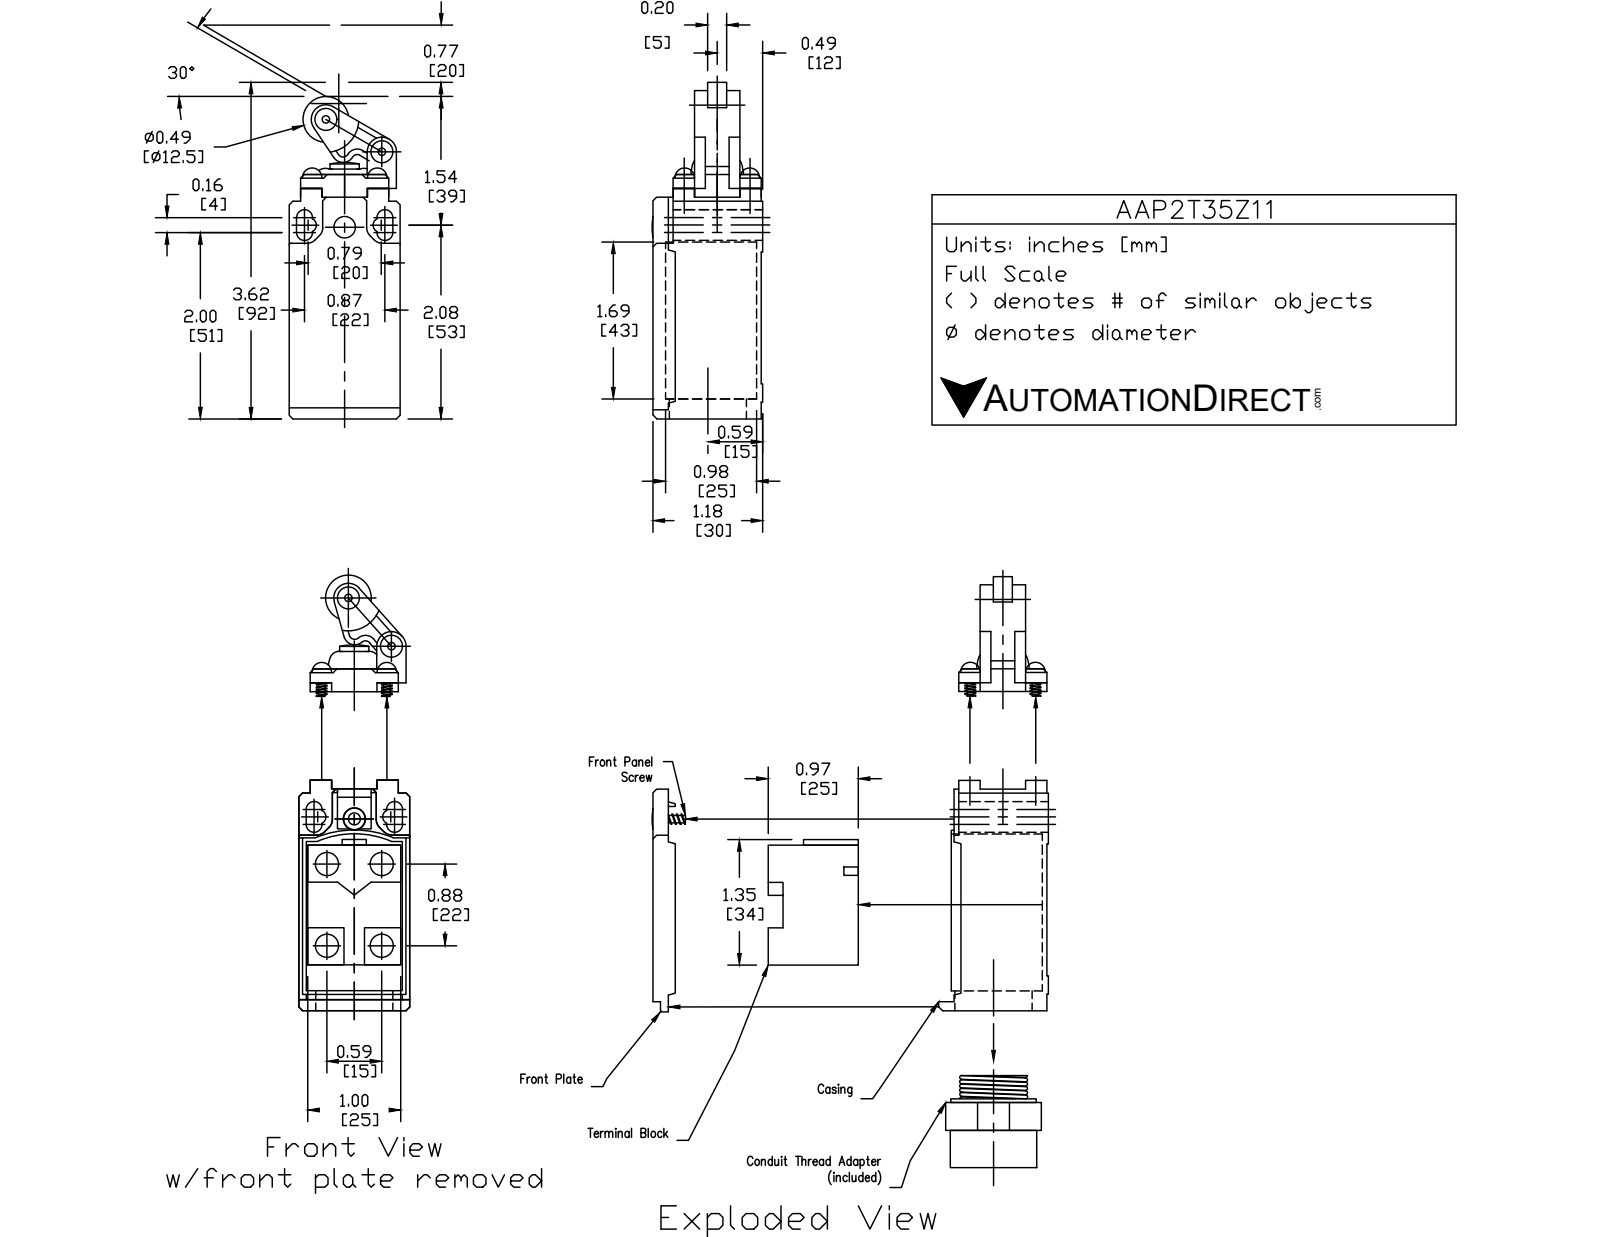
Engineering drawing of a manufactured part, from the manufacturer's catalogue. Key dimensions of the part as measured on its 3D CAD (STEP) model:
Part name (STEP PRODUCT): AAP2T35Z11
STEP written by: SolidWorks 2017 (AUTOMOTIVE_DESIGN)
Units: inches
Bodies: 6 solids, 271 faces (151 planar, 90 cylindrical, 30 other)
Overall size (bounding box): 3.621 × 1.205 × 1.193
Volume: 3.513 in³ · Surface area: 23.91 in²
Round holes (diameter × count): ⌀0.236 ×1, ⌀0.319 ×1, ⌀0.571 ×1, ⌀0.669 ×1, ⌀0.748 ×1
Round bosses / shafts (diameter × count): ⌀0.22 ×5, ⌀0.563 ×1, ⌀0.492 ×1, ⌀0.315 ×1, ⌀0.307 ×1, ⌀0.276 ×1, ⌀0.256 ×1
Partial cylindrical surfaces — rounded edges, fillets, slot ends (radius × count): R0.039 ×8, R0.118 ×8, R0.079 ×6, R0.059 ×2, R0.138 ×2, R0.157 ×2, R0.165 ×2, R0.287 ×1
Main face-to-face distances: 1.193, 1.165, 0.236, 0.016, 2.406, 1.181, 0.945, 0.039, 2.61, 0.205
Hole centre spacings: 0.083
